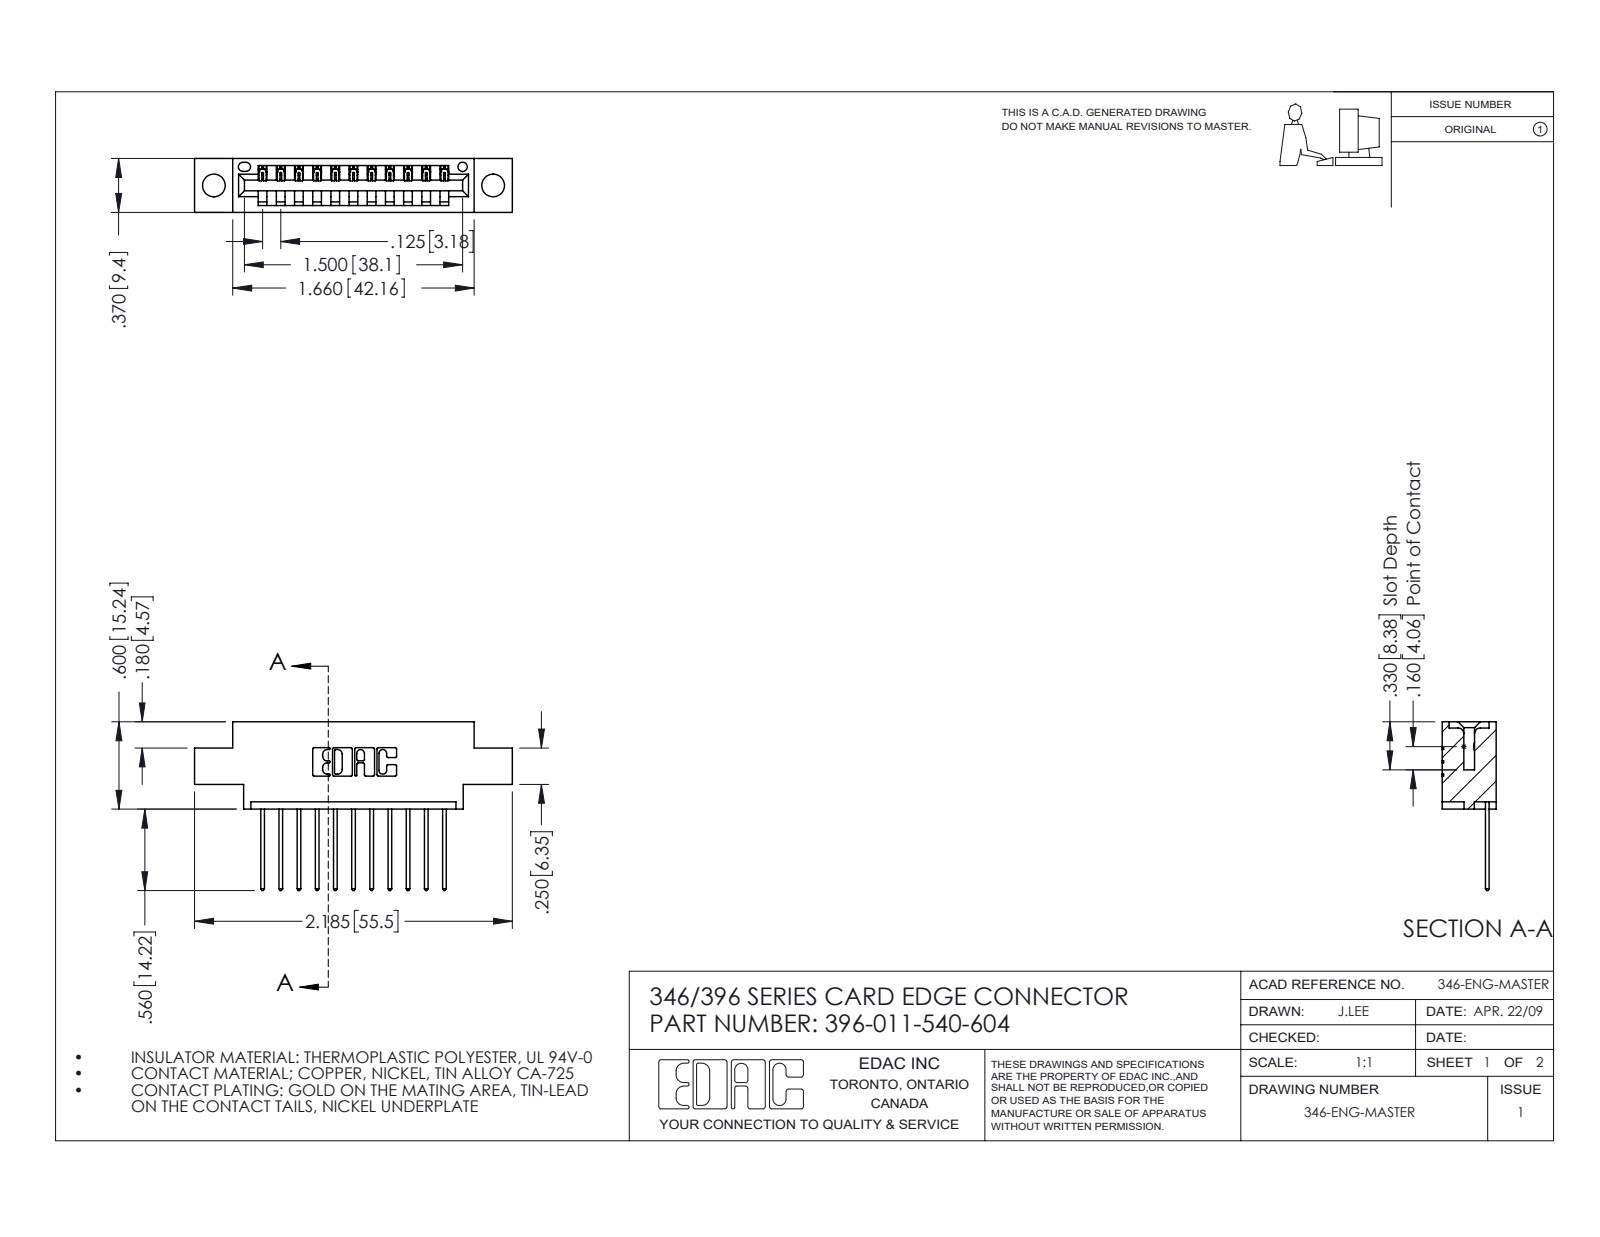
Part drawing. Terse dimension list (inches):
name: 345-292-001_345-293-140; 396-011-540-604; 346 Part_0.170 Offset - 0.156 Dia-TH
written by: SolidWorks 2016 (CONFIG_CONTROL_DESIGN)
unit: in
bodies: 12 solids, 764 faces (520 planar, 244 cylindrical, 0 other)
size: 2.185 × 1.16 × 0.37
volume: 0.297 in³; area: 9.034 in²
holes: 2× ⌀0.156, 1× ⌀0.064
rounds: 22× R0.006, 22× R0.01, 22× R0.01, 6× R0.007, 6× R0.031, 3× R0.026, 2× R0.031, 2× R0.04
face distances: 0.25, 0.37, 0.048, 0.322, 0.072, 0.298, 0.025, 0.148, 0.222, 0.1
hole spacings: 0.246, 1.715, 1.92
